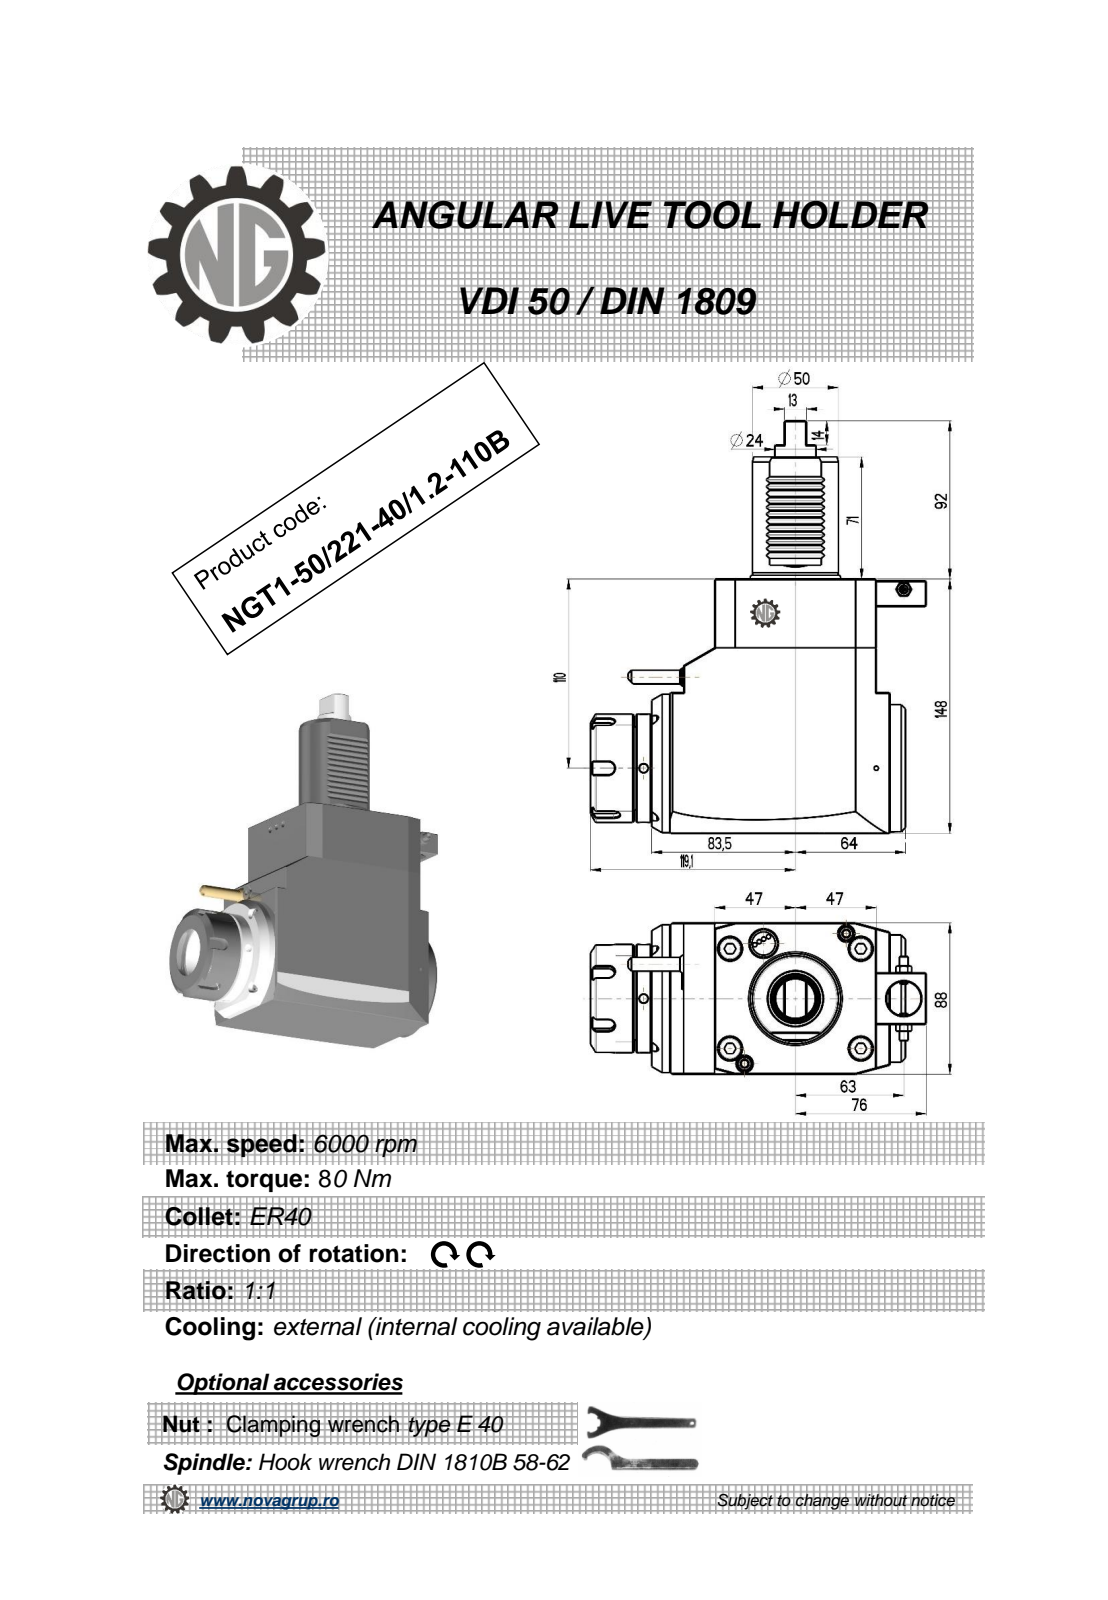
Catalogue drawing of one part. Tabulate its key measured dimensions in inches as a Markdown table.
| quantity | value |
| --- | --- |
| part name | NGT1_50_221_40_1_2_110B |
| STEP written by | PRO/ENGINEER BY PARAMETRIC TECHNOLOGY CORPORATION, 2010280 (CONFIG_CONTROL_DESIGN) |
| units | inches |
| bodies | 1 solid, 431 faces (210 planar, 99 cylindrical, 122 other) |
| overall size | 9.449 × 7.681 × 3.465 |
| volume | 111.6 in³ |
| surface area | 176.8 in² |
| round holes (diameter × count) | 0.197 × 3, 0.15 × 2, 0.157 × 2, 0.118 × 1, 0.374 × 1, 0.787 × 1, 1.319 × 1 |
| round bosses / shafts (diameter × count) | 3.386 × 1, 2.913 × 1, 2.48 × 1, 2.008 × 1, 1.969 × 1, 0.945 × 1, 0.394 × 1, 0.353 × 1 |
| partial cylindrical surfaces (radius × count) | 0.01 × 12, 0.012 × 12, 0.008 × 6, 0.148 × 5, 0.031 × 2, 0.098 × 1 |
| main face-to-face distances | 3.465, 5.827, 5.807, 0.669, 0.315, 3.701, 4.37, 0.354, 1.437, 5.138 |
| hole center spacings | 0.354, 4.012, 0.709, 1.958, 2.065, 2.225, 2.23, 3.996 |
